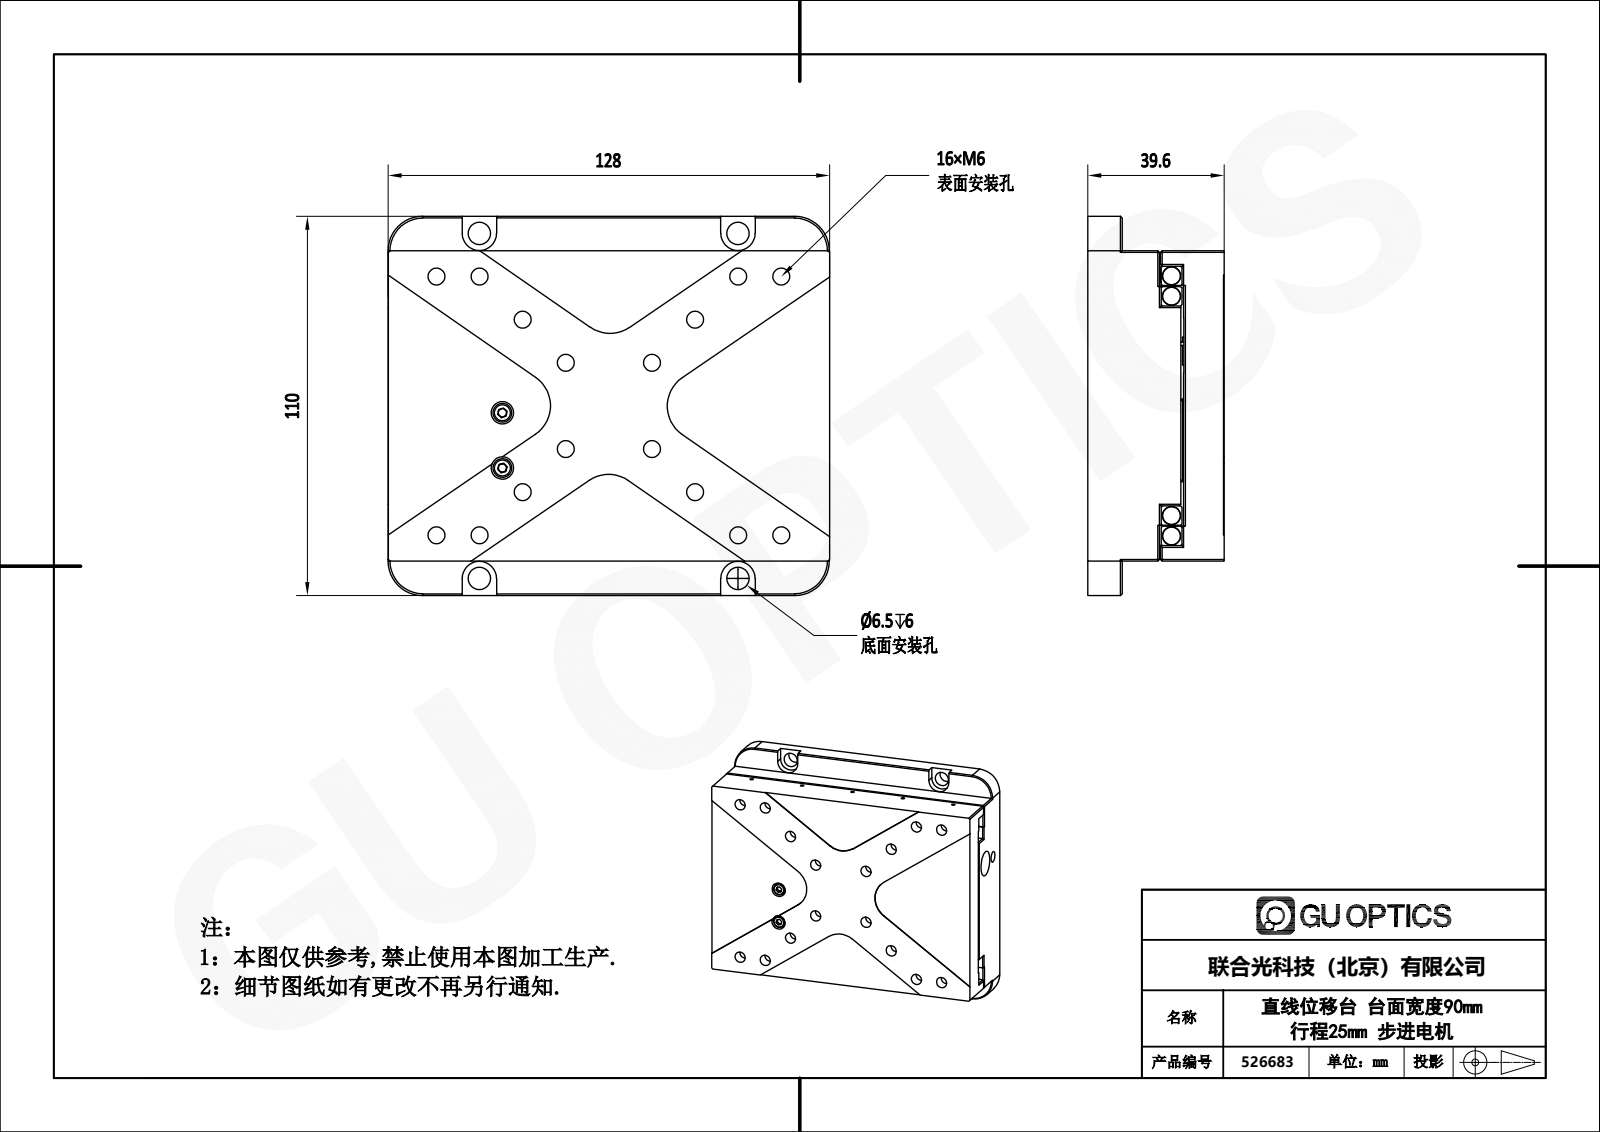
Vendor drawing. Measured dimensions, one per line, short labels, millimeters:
name: FMS90R-25_1
written by: SolidWorks 2020 (CONFIG_CONTROL_DESIGN)
unit: mm
bodies: 0 solids, 2881 faces (1773 planar, 629 cylindrical, 479 other)
size: 128.06 × 110 × 39.6
holes: 46× ⌀2.5, 35× ⌀2.55, 32× ⌀4.4, 19× ⌀1.6, 17× ⌀5, 10× ⌀2.4, 8× ⌀2, 6× ⌀6.5, 5× ⌀6, 4× ⌀1.25, 4× ⌀3.35, 4× ⌀3.4
bosses: 44× ⌀2, 26× ⌀1, 16× ⌀3, 12× ⌀5.5, 7× ⌀2.5, 4× ⌀4.5, 4× ⌀4.4, 4× ⌀1.6
rounds: 26× R1, 20× R2, 16× R0.3, 14× R0.2, 10× R1.1, 8× R0.4, 8× R0.8, 8× R2.1
face distances: 0.5, 27.8, 10, 6.5, 18.3, 39.4, 11.6, 6, 5, 2.5
hole spacings: 4.76, 8.5, 9.5, 12.75, 17.39, 15, 9.26, 12.38
